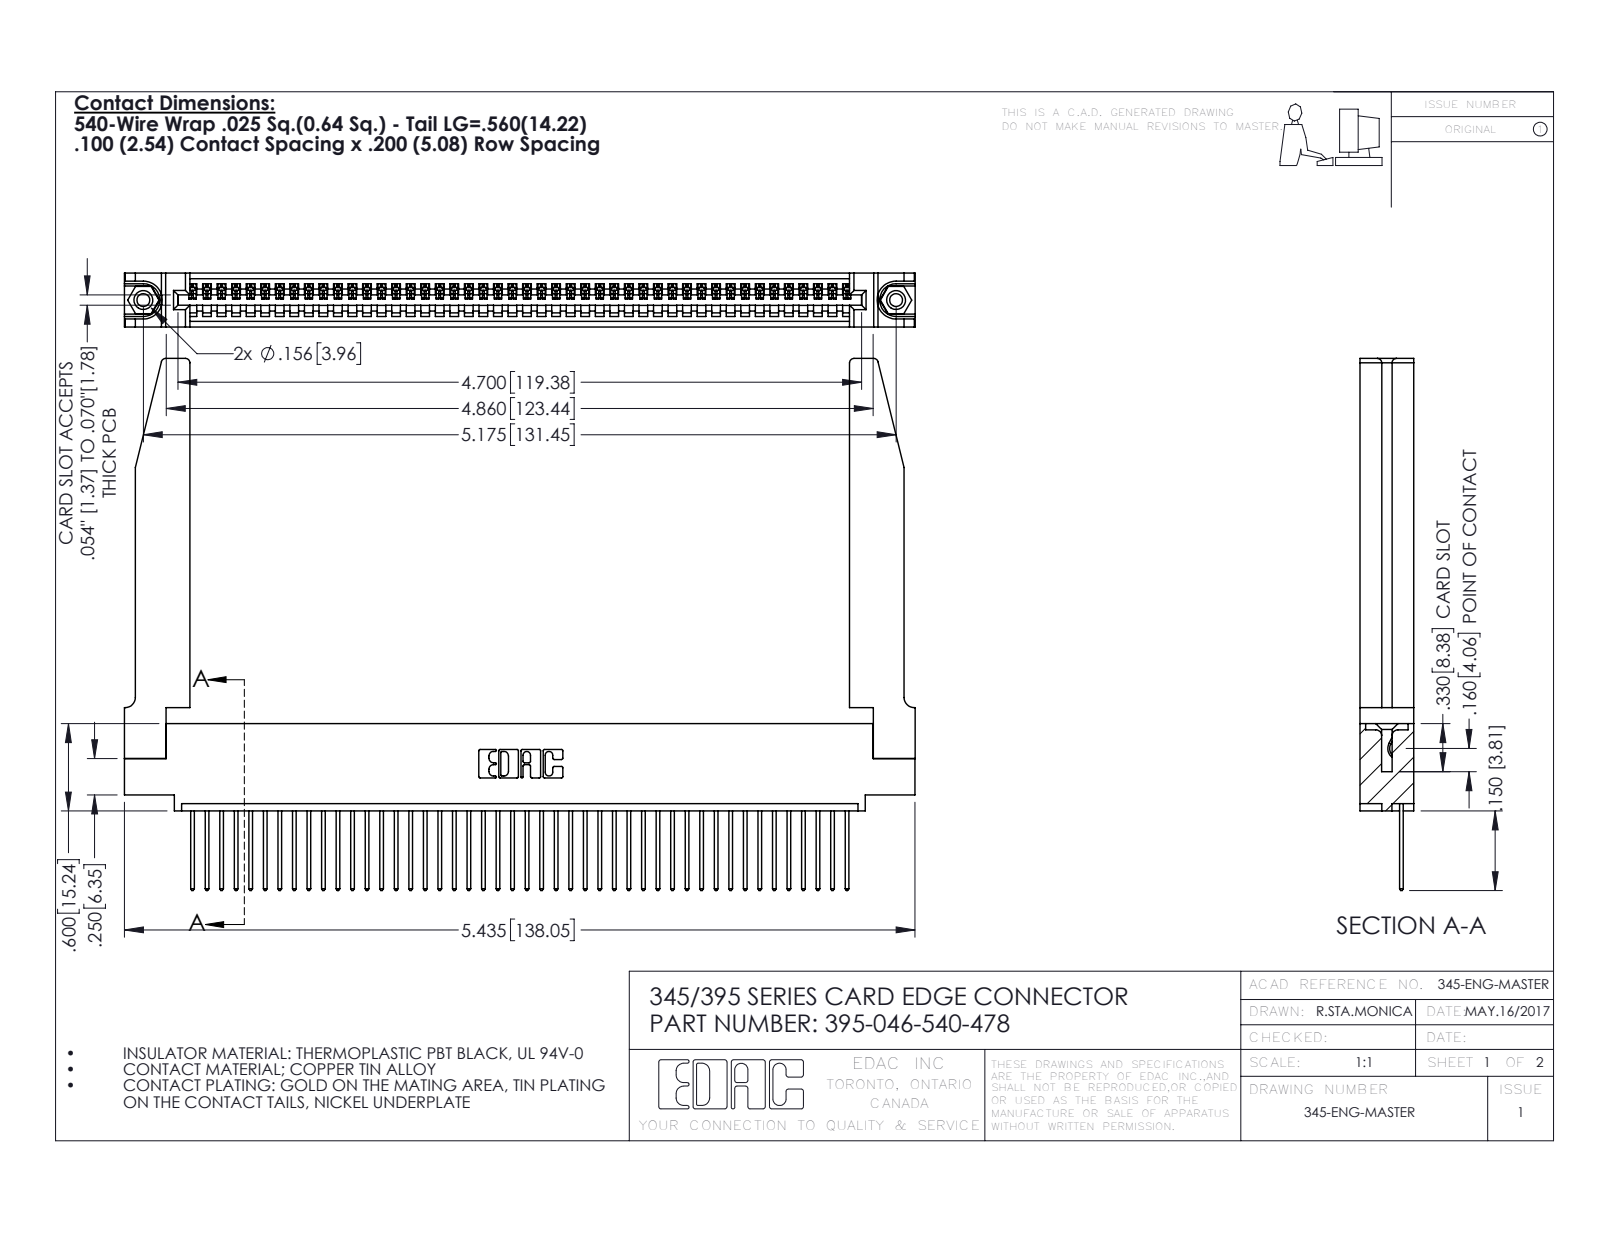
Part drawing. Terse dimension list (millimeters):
name: 345-220-078_345-220-078; 345-250-001_345-250-001-102; 345 Part_0.110 Offset - 0.156 Dia-TH; 345-292-001_345-293-140 (+1 more)
written by: SolidWorks 2016 (CONFIG_CONTROL_DESIGN)
unit: mm
bodies: 51 solids, 3032 faces (2066 planar, 914 cylindrical, 52 other)
size: 138.1 × 92.9 × 9.4
volume: 20 910 mm³; area: 24 880 mm²
holes: 2× ⌀2.3, 2× ⌀3.2, 2× ⌀4, 1× ⌀1.6
bosses: 2× ⌀3.9
rounds: 92× R0.2, 92× R0.3, 22× R0.3, 8× R0.8, 6× R0.2, 6× R0.8, 3× R0.7, 2× R0.8
face distances: 1.8, 9.4, 7.6, 2.5, 6.9, 0.6, 5.1, 5.7, 3.8, 3.8
hole spacings: 6.9, 125.5, 131.4
